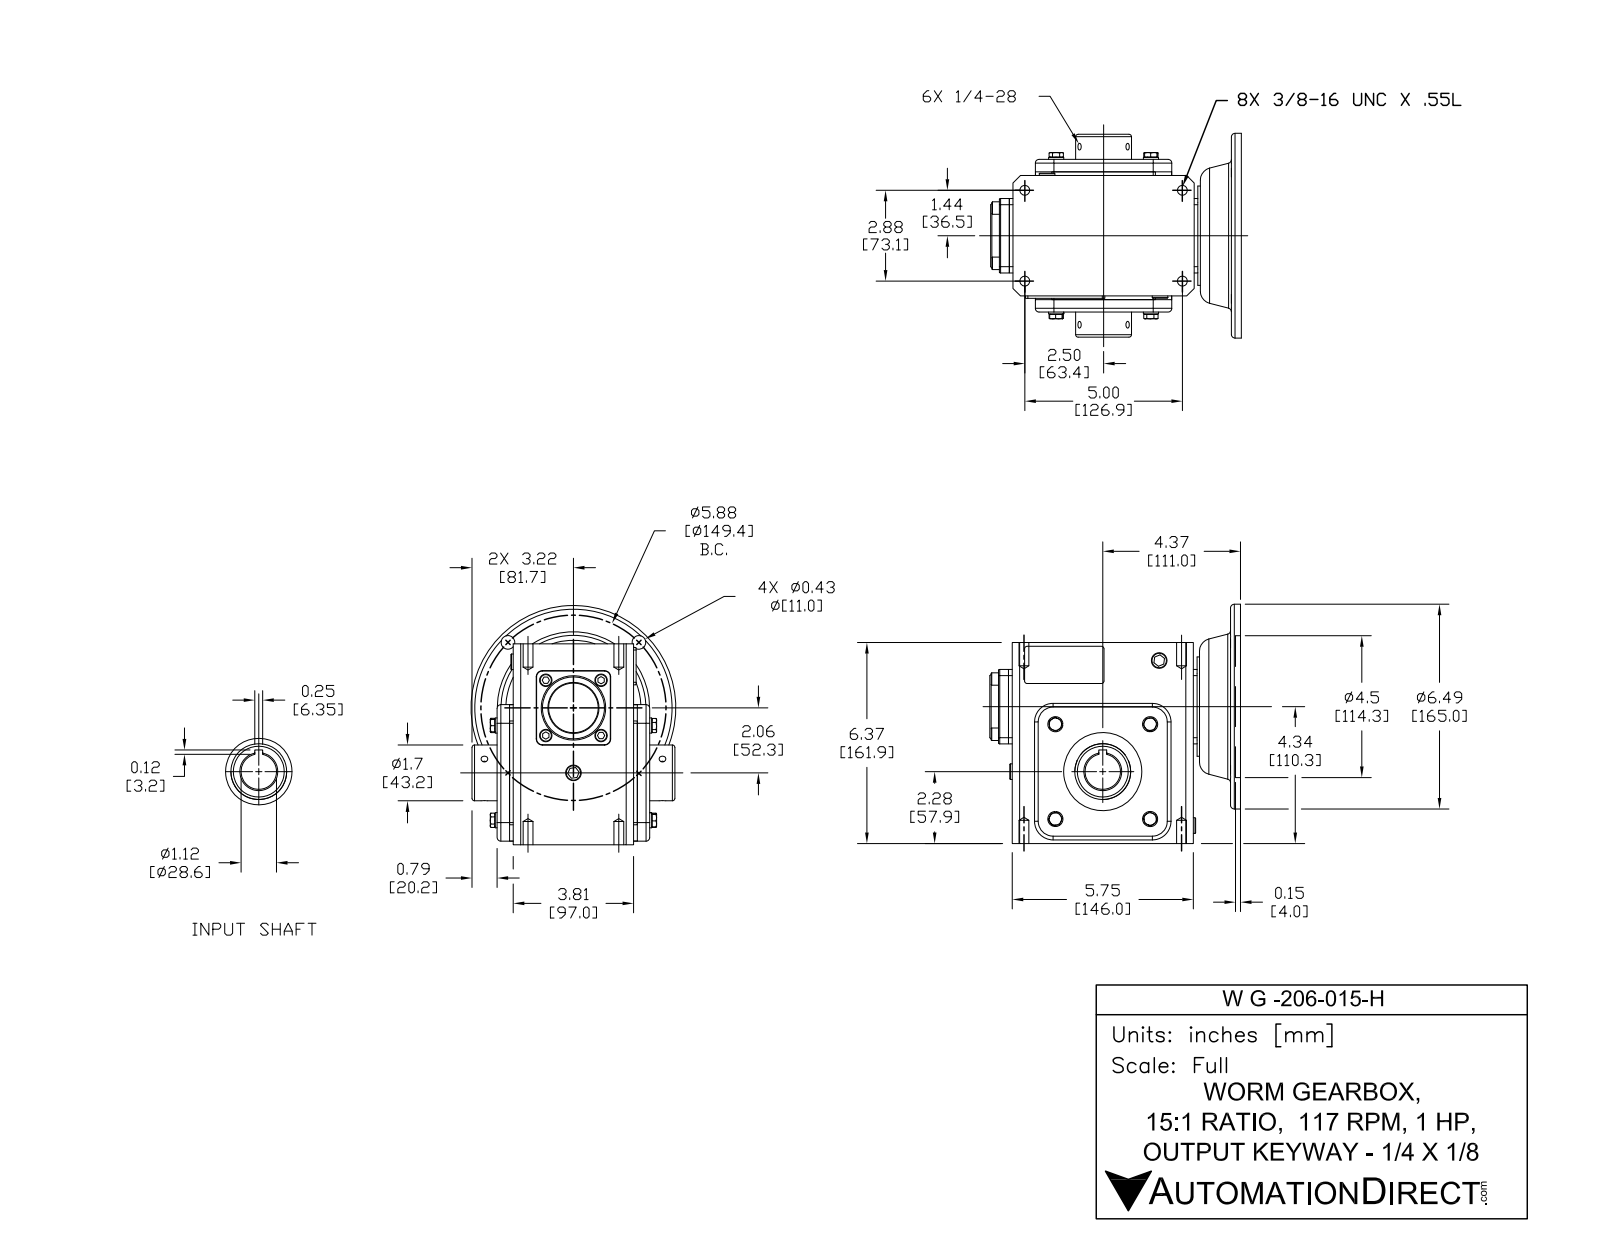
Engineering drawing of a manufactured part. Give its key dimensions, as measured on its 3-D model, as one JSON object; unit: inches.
{"part_name": "WG-206-015-H", "step_written_by": "SolidWorks 2015 (CONFIG_CONTROL_DESIGN)", "units": "inches", "bodies": {"solids": 45, "faces": 628, "planar": 304, "cylindrical": 198, "other": 126}, "overall_size": [7.953, 7.591, 6.496], "volume_in3": 171, "surface_area_in2": 463.1, "round_holes": [[0.213, 6], [0.313, 4], [0.406, 4], [0.591, 1], [0.625, 1], [1.125, 1], [1.457, 1], [1.772, 1], [2.402, 1], [3.543, 1], [4.5, 1]], "round_bosses_or_shafts": [[0.394, 8], [0.48, 4], [6.496, 1], [3.15, 1], [2.047, 1], [1.575, 1], [1.181, 1], [1.142, 1]], "partial_cylinders_radius": [[0.079, 8], [0.118, 8], [0.197, 4], [0.591, 4], [0.02, 2], [0.039, 2], [2.717, 1]], "face_to_face_distances": [0.118, 4.055, 0.394, 4.331, 3.937, 0.512, 4.449, 6.375, 5.866, 1.181], "hole_center_spacings": [2.858, 2.937, 4.154, 4.943, 5.65, 2.077, 2.88, 4.631]}
